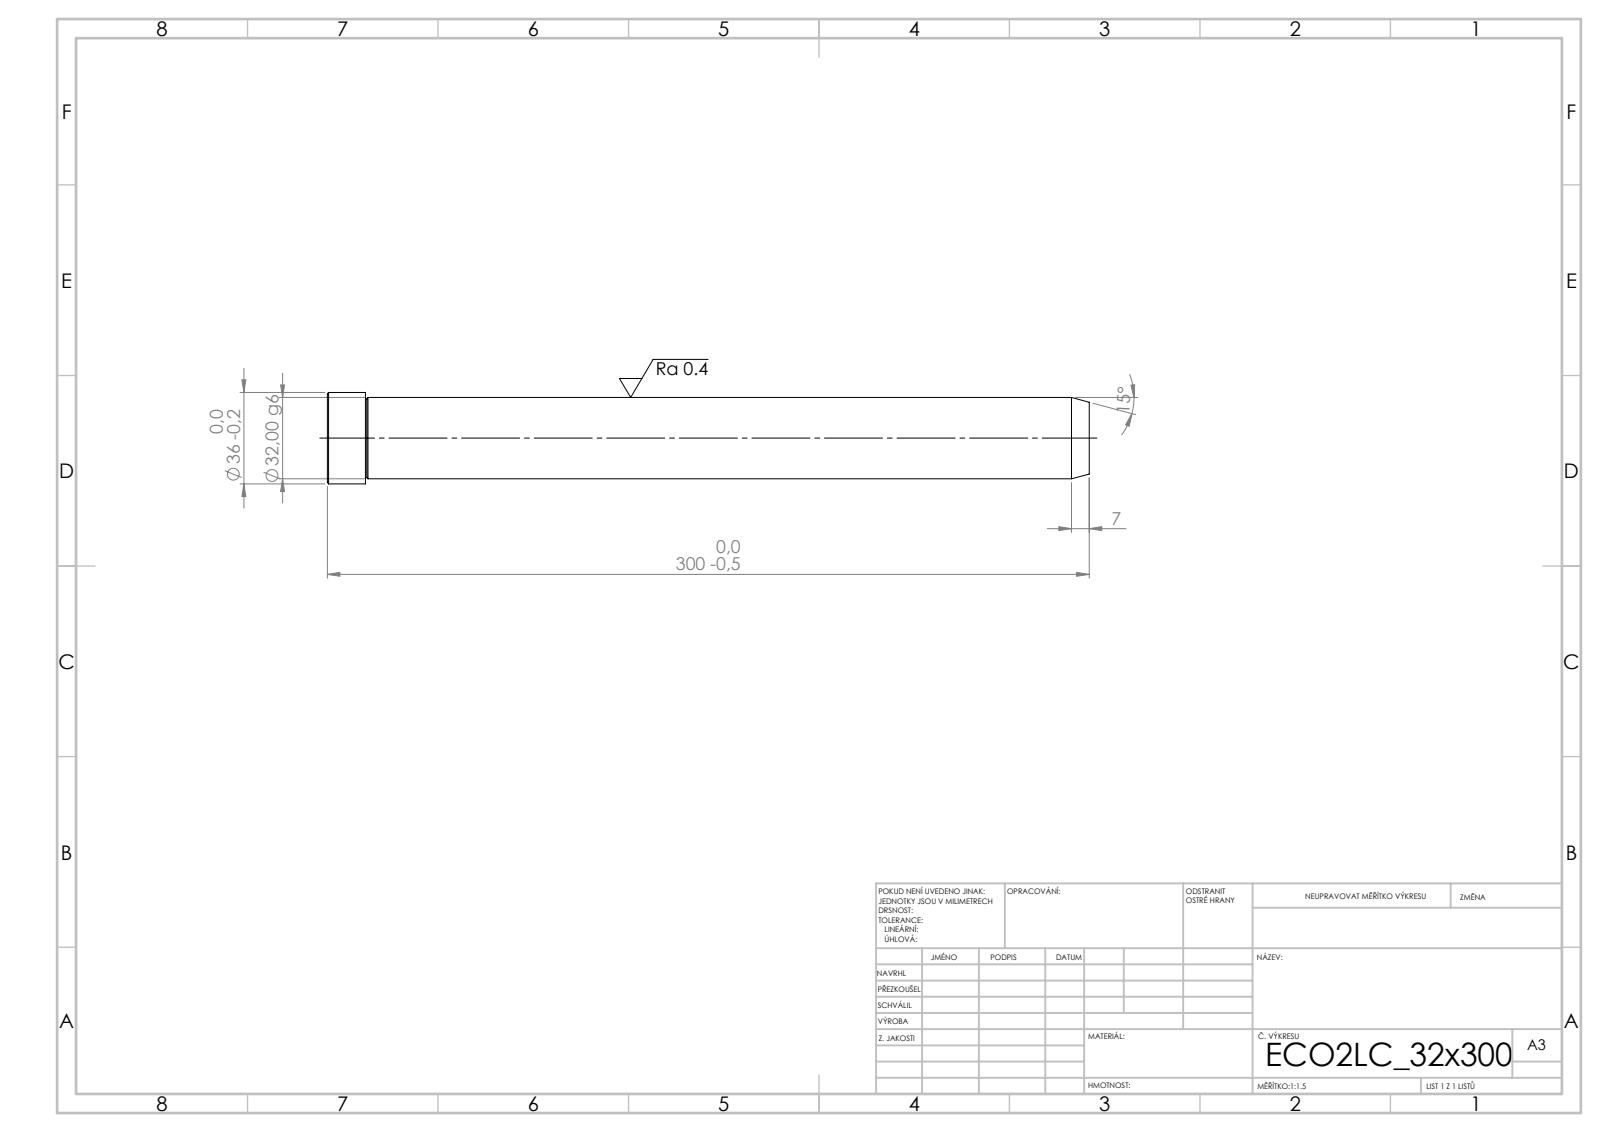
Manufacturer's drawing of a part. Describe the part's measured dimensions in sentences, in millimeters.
Its 3-D file was written by "SolidWorks 2019 (CONFIG_CONTROL_DESIGN)". It is 1 solid with 15 faces: 3 planar, 4 cylindrical and 8 other. Overall it measures 300 by 36 by 36 millimeters. Its volume is 243 792 cubic millimeters and its surface area 32 209 square millimeters. Round bosses or shafts: 1 of diameter 36, 1 of diameter 32. The main face-to-face distances are 300, 285, 15.
